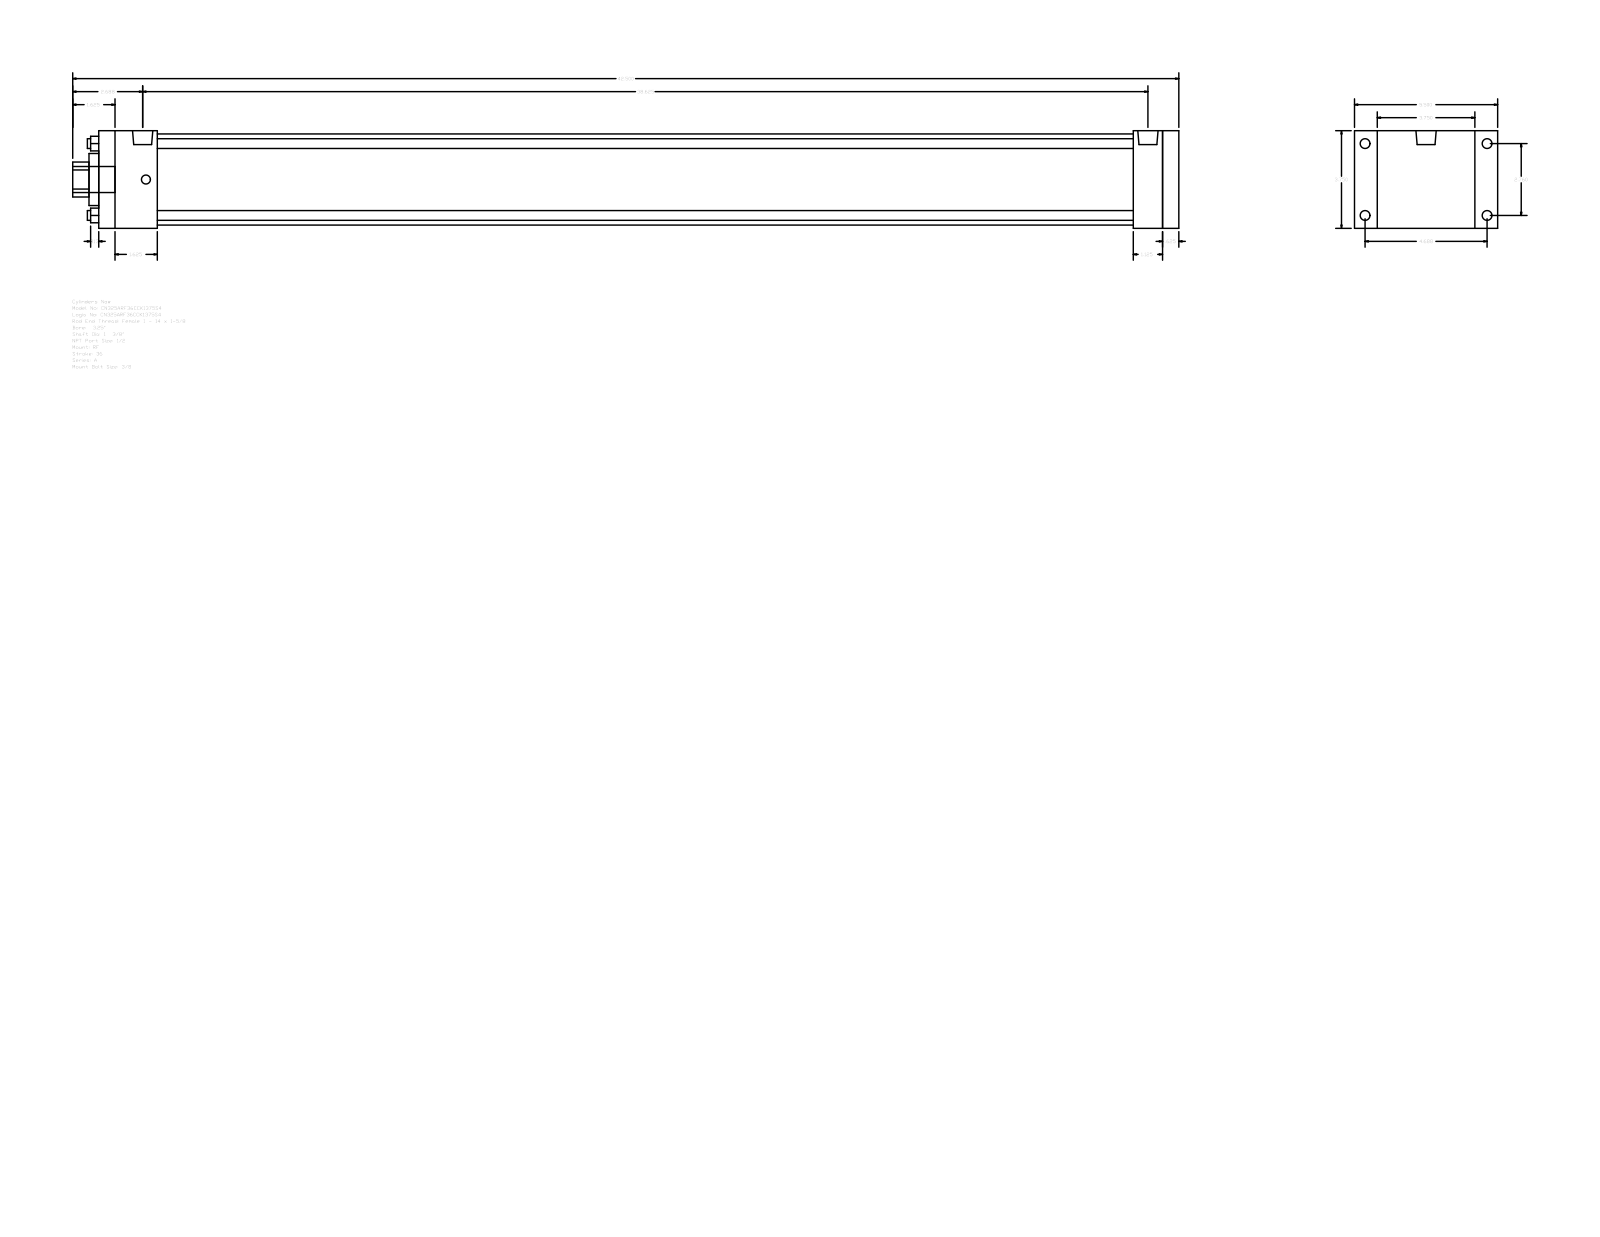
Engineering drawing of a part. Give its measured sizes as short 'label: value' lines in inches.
name: A_RF__0325_1.375
written by: GSSL Pune (CONFIG_CONTROL_DESIGN)
unit: in
bodies: 0 solids, 92 faces (64 planar, 28 cylindrical, 0 other)
size: 42.5 × 5.5 × 3.75
holes: 4× ⌀0.375, 1× ⌀1.375, 1× ⌀2, 1× ⌀3.5
bosses: 4× ⌀0.375, 4× ⌀0.344, 2× ⌀0.778, 1× ⌀1
rounds: 1× R0.672
face distances: 3.75, 41.5, 0.625, 40.875, 0.875, 4.625, 1.125, 39.75, 1.75, 2.25
hole spacings: 1.952, 2.76, 3.903
